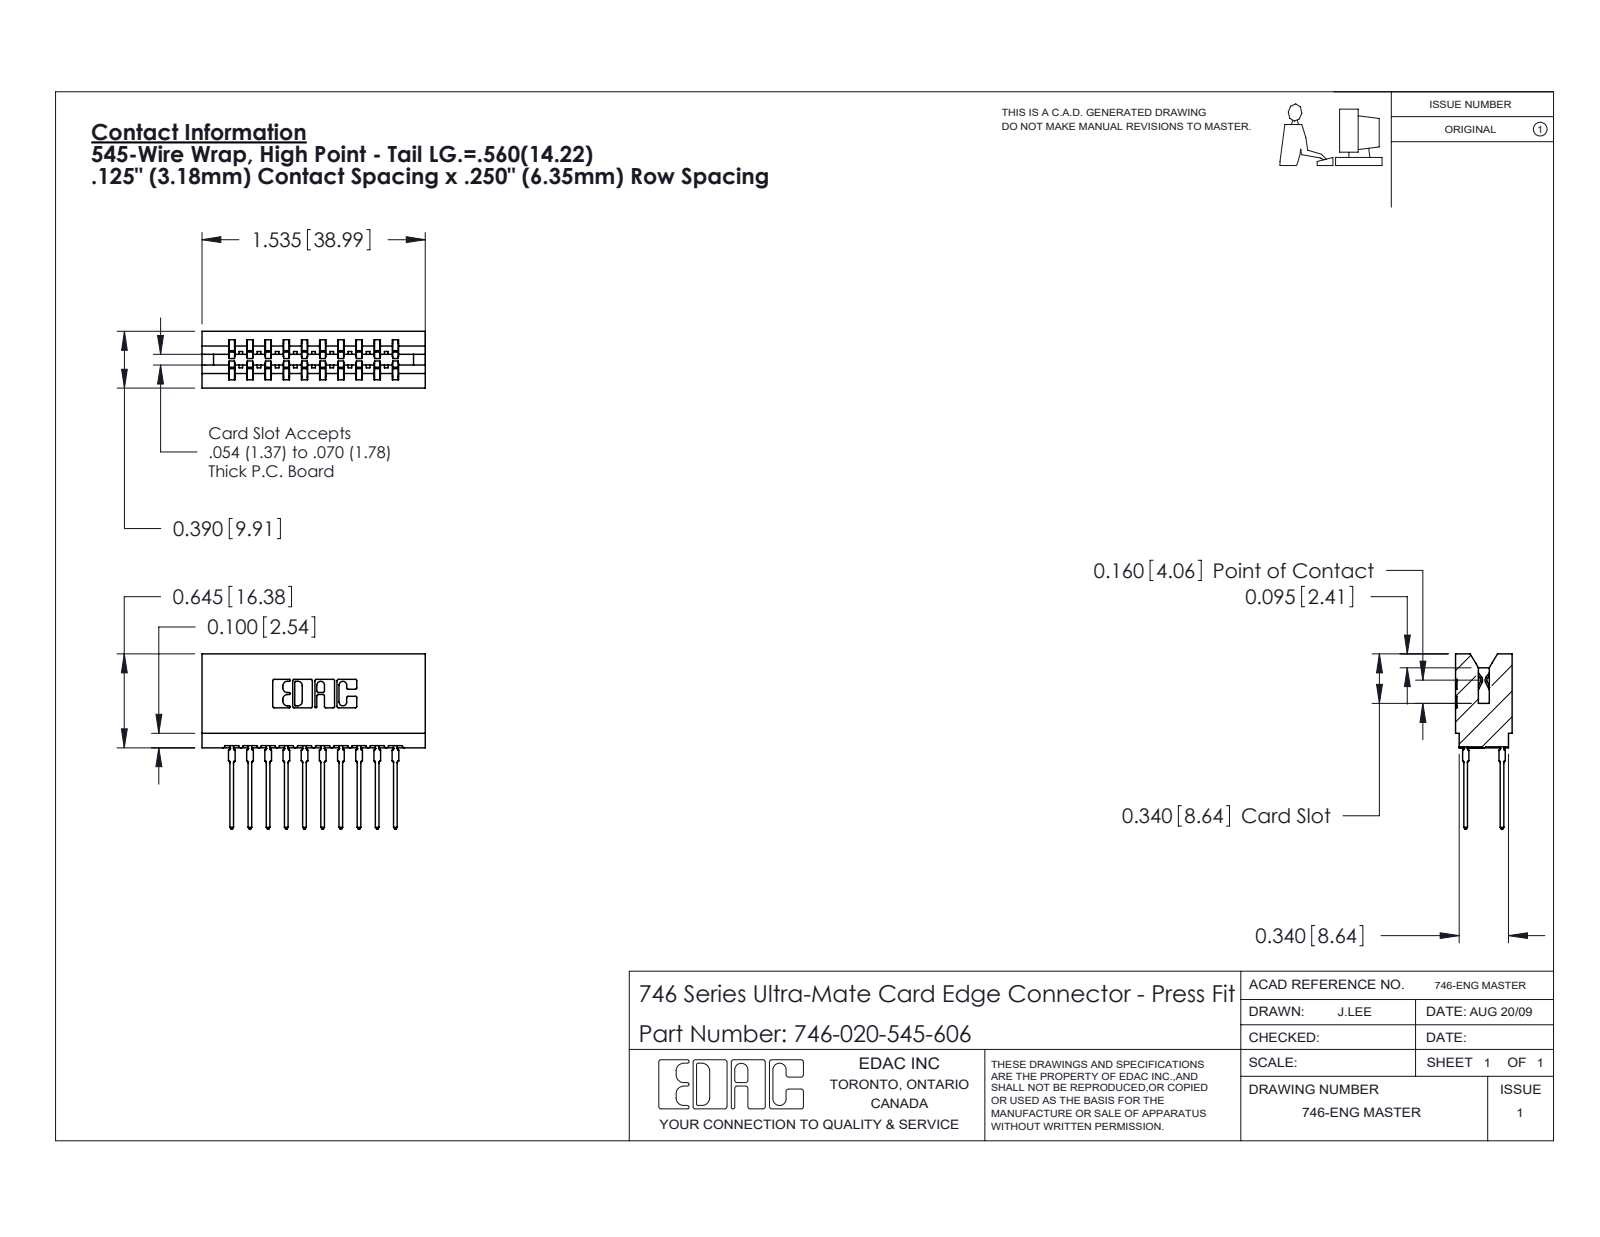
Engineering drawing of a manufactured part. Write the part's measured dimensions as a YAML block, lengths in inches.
part_name: "746 Part_.340 Slot Depth - 06; 746-292-001_545; 746-020-545-606"
step_written_by: "SolidWorks 2020 (CONFIG_CONTROL_DESIGN)"
units: inches
bodies: {solids: 21, faces: 1888, planar: 976, cylindrical: 392, other: 520}
overall_size: [1.535, 1.204, 0.39]
volume: 0.287
surface_area: 10.33
partial_cylinders:
  - {radius: 0.021, count: 40}
  - {radius: 0.01, count: 22}
  - {radius: 0.015, count: 11}
  - {radius: 0.005, count: 8}
  - {radius: 0.011, count: 8}
  - {radius: 0.007, count: 6}
  - {radius: 0.031, count: 6}
  - {radius: 0.026, count: 3}
face_to_face_distances: [0.25, 0.057, 0.333, 0.5, 0.042, 0.125, 0.75, 0.125, 0.083, 0.39]
